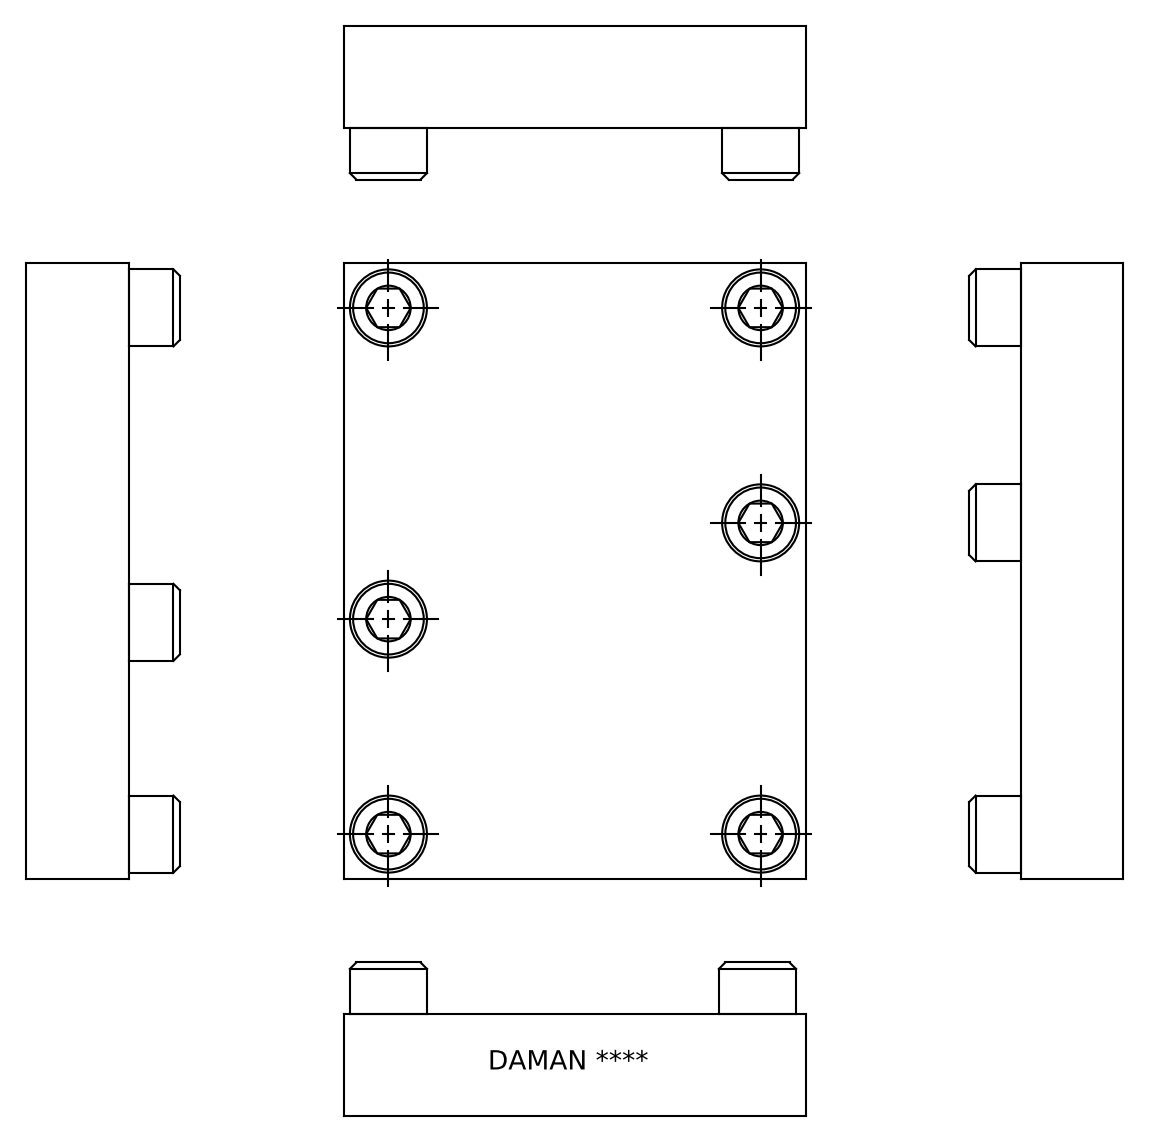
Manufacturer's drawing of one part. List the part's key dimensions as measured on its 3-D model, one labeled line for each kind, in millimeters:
Part name (STEP PRODUCT): Part_AD08CPP.B00021R11_3D
STEP written by: Autodesk Inventor 2022 (AUTOMOTIVE_DESIGN)
Units: millimetres
Bodies: 1 solid, 301 faces (206 planar, 14 cylindrical, 81 other)
Overall size (bounding box): 152.4 × 114.3 × 25.4
Volume: 407 545 mm³ · Surface area: 55 083 mm²
Round holes (diameter × count): ⌀13.49 ×6, ⌀33.35 ×4, ⌀6.35 ×2, ⌀25.4 ×2
Main face-to-face distances: 25.4, 2.79, 22.61, 114.3, 152.4, 152.36, 3.62, 0.64, 3.66, 9.1
Hole centre spacings: 29.52, 29.53, 34.16, 47.62, 61.92, 80.19, 102.31, 125.42
